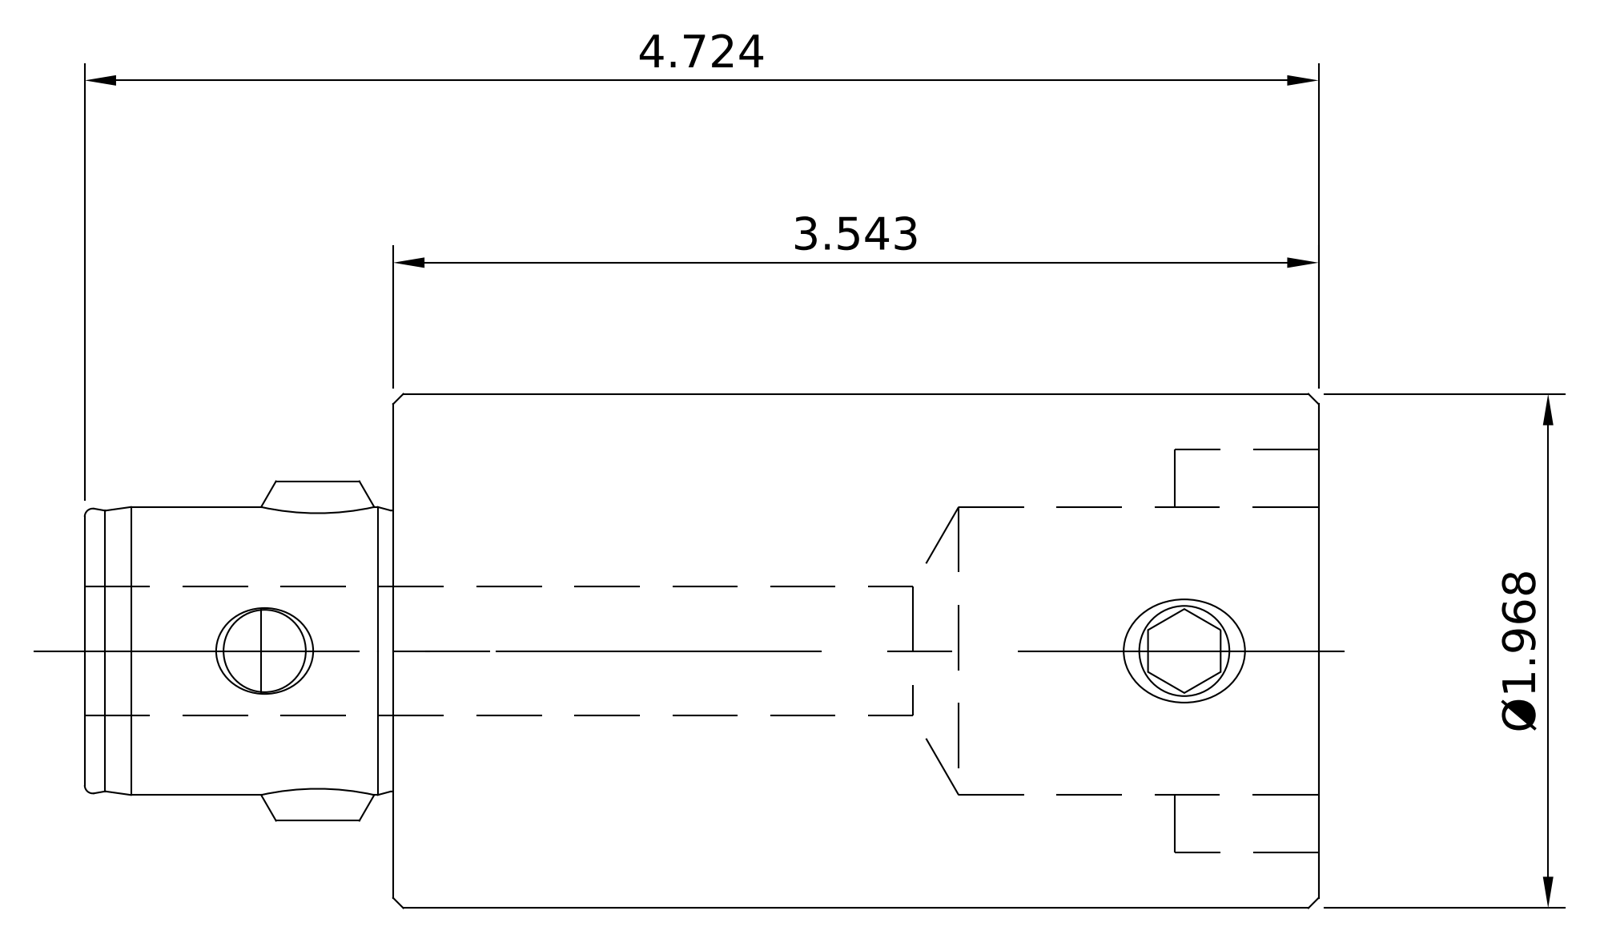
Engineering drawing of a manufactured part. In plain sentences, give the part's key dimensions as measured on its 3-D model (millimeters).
The part is named "11.331.551; 10.690.43X_10.690.435; 10.691.50X_10.691.505; 691-50XRing_10.691.505Ring (+1 more)". Its 3-D file was written by "SolidWorks 2016 (AUTOMOTIVE_DESIGN)". It is 4 solids with 142 faces: 39 planar, 47 cylindrical and 56 other. Overall it measures 120 by 50 by 50 millimeters. Its volume is 154 576 cubic millimeters and its surface area 30 420 square millimeters. Round holes: 1 of diameter 4.5, 1 of diameter 8, 1 of diameter 8.5, 1 of diameter 10.3, 1 of diameter 11, 1 of diameter 12.5, 1 of diameter 14.5, 1 of diameter 22, 1 of diameter 28, 1 of diameter 28.5. Round bosses or shafts: 1 of diameter 50, 1 of diameter 49.6, 1 of diameter 10.9, 1 of diameter 10, 1 of diameter 8.8, 1 of diameter 6.9. Partial cylindrical surfaces (rounded edges, fillets, slot ends): 2 of radius 4.5, 1 of radius 14. The main face-to-face distances are 90, 30, 120, 85, 55, 35, 24.1, 106.4, 76.4, 21.4. The hole center spacings are 19.5, 89.45.
